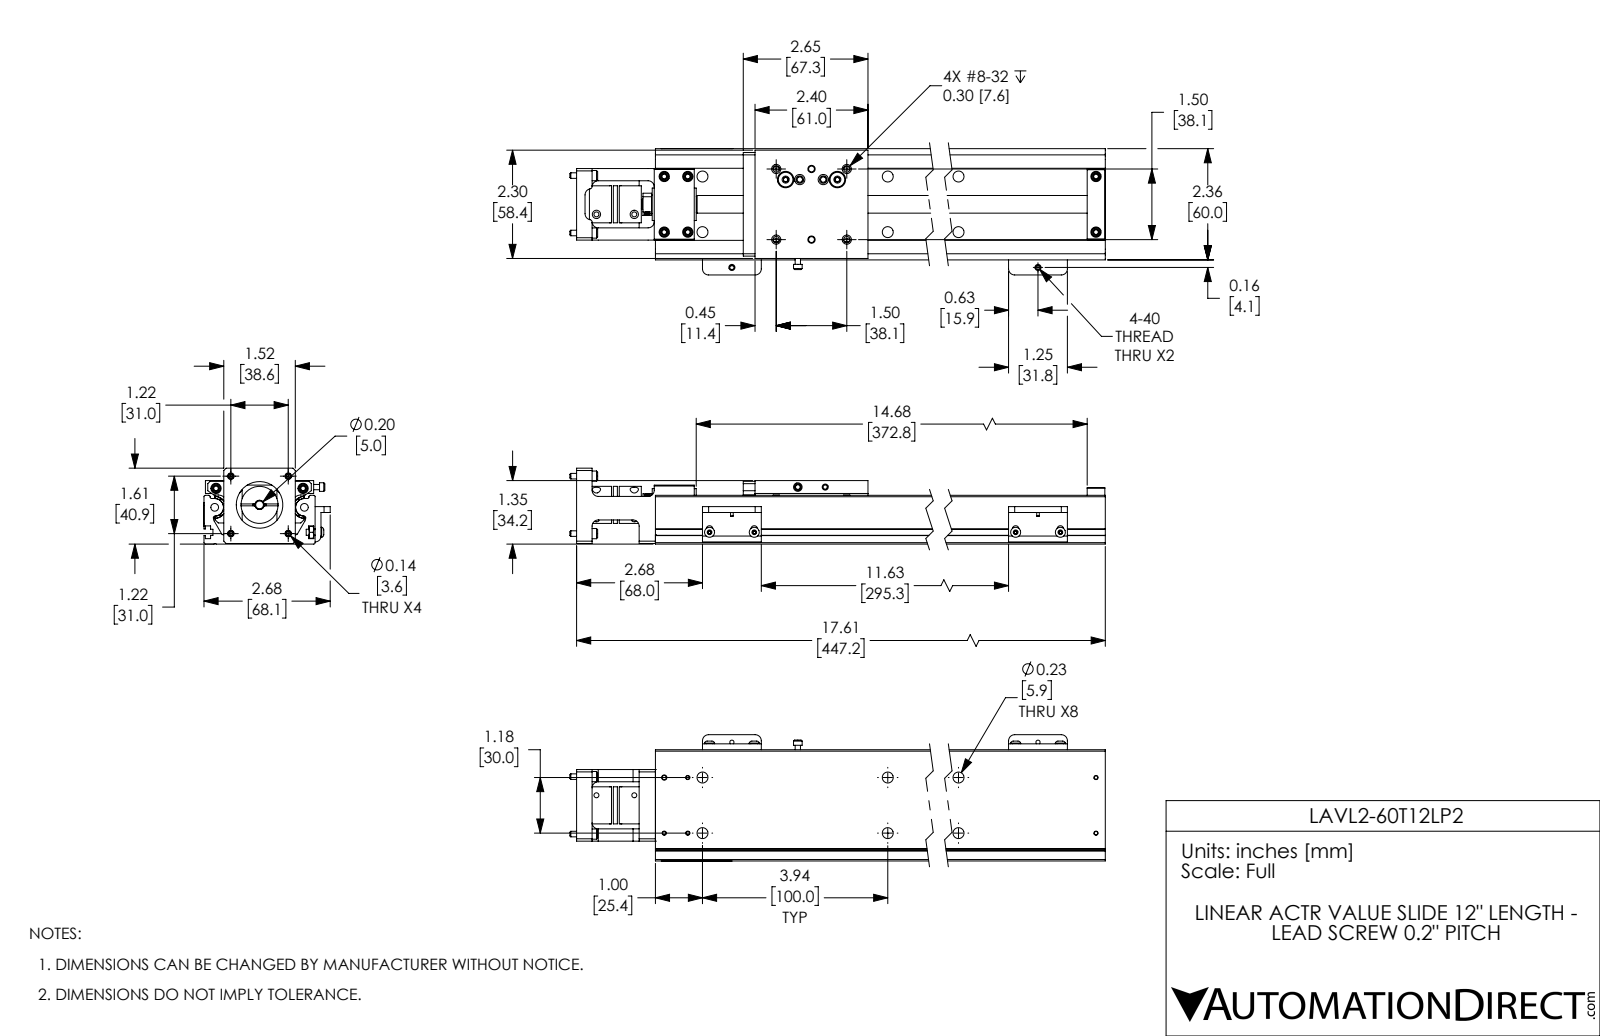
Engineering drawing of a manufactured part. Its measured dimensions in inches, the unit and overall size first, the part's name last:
Units: inches
Overall size (bounding box): 17.748 × 2.683 × 1.612
Round holes (diameter × count): ⌀0.089 ×18, ⌀0.141 ×10, ⌀0.219 ×10, ⌀0.234 ×8, ⌀0.136 ×6, ⌀0.141 ×4, ⌀0.03 ×2, ⌀0.1 ×2, ⌀0.106 ×2, ⌀0.125 ×2, ⌀0.159 ×2, ⌀0.165 ×2
Round bosses / shafts (diameter × count): ⌀0.112 ×15, ⌀0.183 ×11, ⌀0.217 ×4, ⌀0.213 ×4, ⌀0.118 ×4, ⌀0.312 ×2, ⌀0.19 ×2, ⌀0.164 ×2
Partial cylindrical surfaces — rounded edges, fillets, slot ends (radius × count): R0.13 ×20, R0.03 ×12, R0.07 ×8, R0.06 ×4, R0.02 ×3, R0.04 ×2, R0.05 ×2, R0.065 ×2
Main face-to-face distances: 0.2, 2.362, 0.14, 0.115, 0.185, 1.348, 1.148, 2.222, 0.281, 0.421
Hole centre spacings: 1.181, 1.5, 3.937, 4.11, 0.75, 0.863, 1.677, 7.874
Volume: 22.12 in³ · Surface area: 296.8 in²
Bodies: 52 solids, 2128 faces (1295 planar, 525 cylindrical, 308 other)
Part name (STEP PRODUCT): LAVL2-60T12LP2_BLOCK; LAVL2-60T12LP2_BODY; LAVL2-60T12LP2
STEP written by: SolidWorks 2017 (AUTOMOTIVE_DESIGN)
